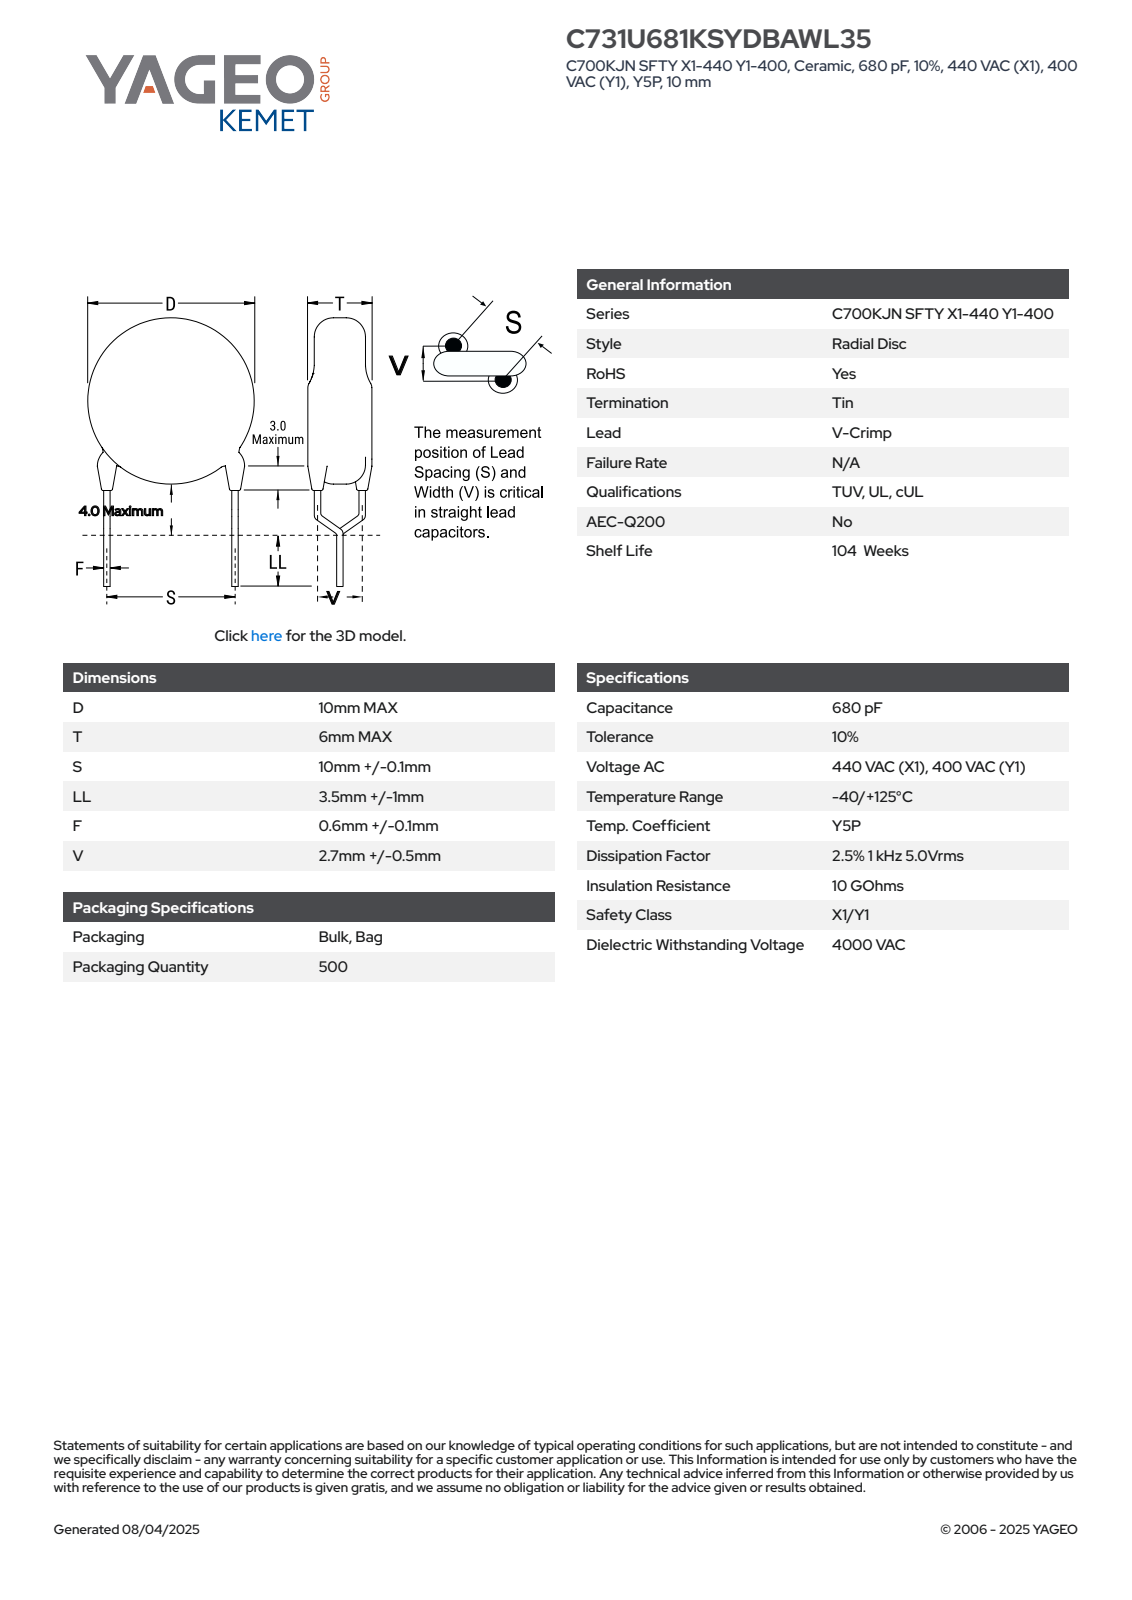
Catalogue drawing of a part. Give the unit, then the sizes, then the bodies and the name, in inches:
Units: inches
Overall size (bounding box): 0.571 × 0.441 × 0.236
Round bosses / shafts (diameter × count): ⌀0.028 ×6, ⌀0.047 ×4, ⌀0.394 ×1
Main face-to-face distances: 0.236, 0.177, 0.405, 0.228, 0.357, 0.18, 0.048, 0.013, 0.039, 0.195
Volume: 0.029 in³ · Surface area: 0.575 in²
Bodies: 4 solids, 89 faces (63 planar, 22 cylindrical, 4 other)
Part name (STEP PRODUCT): CCD_VC10X6_D10T6S10LL4.5F0.7V2.7
STEP written by: SolidWorks 2021 (AUTOMOTIVE_DESIGN)
